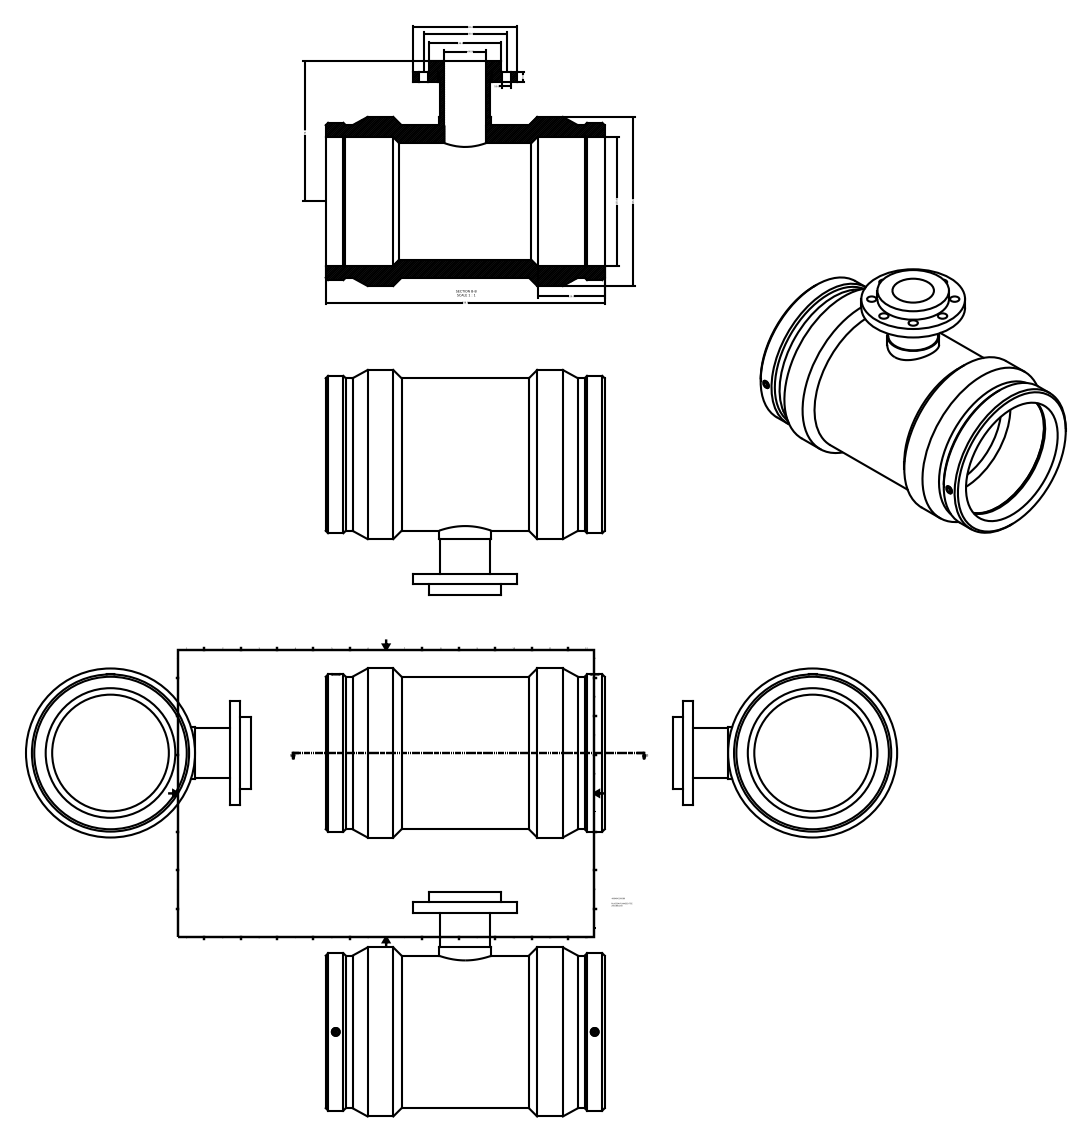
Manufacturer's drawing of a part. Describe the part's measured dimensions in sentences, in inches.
The part is named "499404250080". Its 3-D file was written by "Autodesk Inventor 2015 (AUTOMOTIVE_DESIGN)". It is 1 solid with 60 faces: 14 planar, 30 cylindrical and 16 other. Overall it measures 21.181 by 17.047 by 12.835 inches. Its volume is 962.3 cubic inches and its surface area 1 758 square inches. Round holes: 8 of diameter 0.709, 2 of diameter 0.394, 1 of diameter 3.15, 1 of diameter 4.094, 1 of diameter 8.858, 1 of diameter 9.843. Round bosses or shafts: 2 of diameter 0.157, 1 of diameter 12.835, 1 of diameter 11.936, 1 of diameter 11.578, 1 of diameter 11.551, 1 of diameter 7.874, 1 of diameter 5.433, 1 of diameter 3.937. The main face-to-face distances are 0.787, 21.181, 1.575, 1.483, 19.698, 4.213, 3.425, 2.638, 18.214, 0.551. The hole center spacings are 2.411, 3.15, 4.454, 5.82, 6.299, 19.657.
